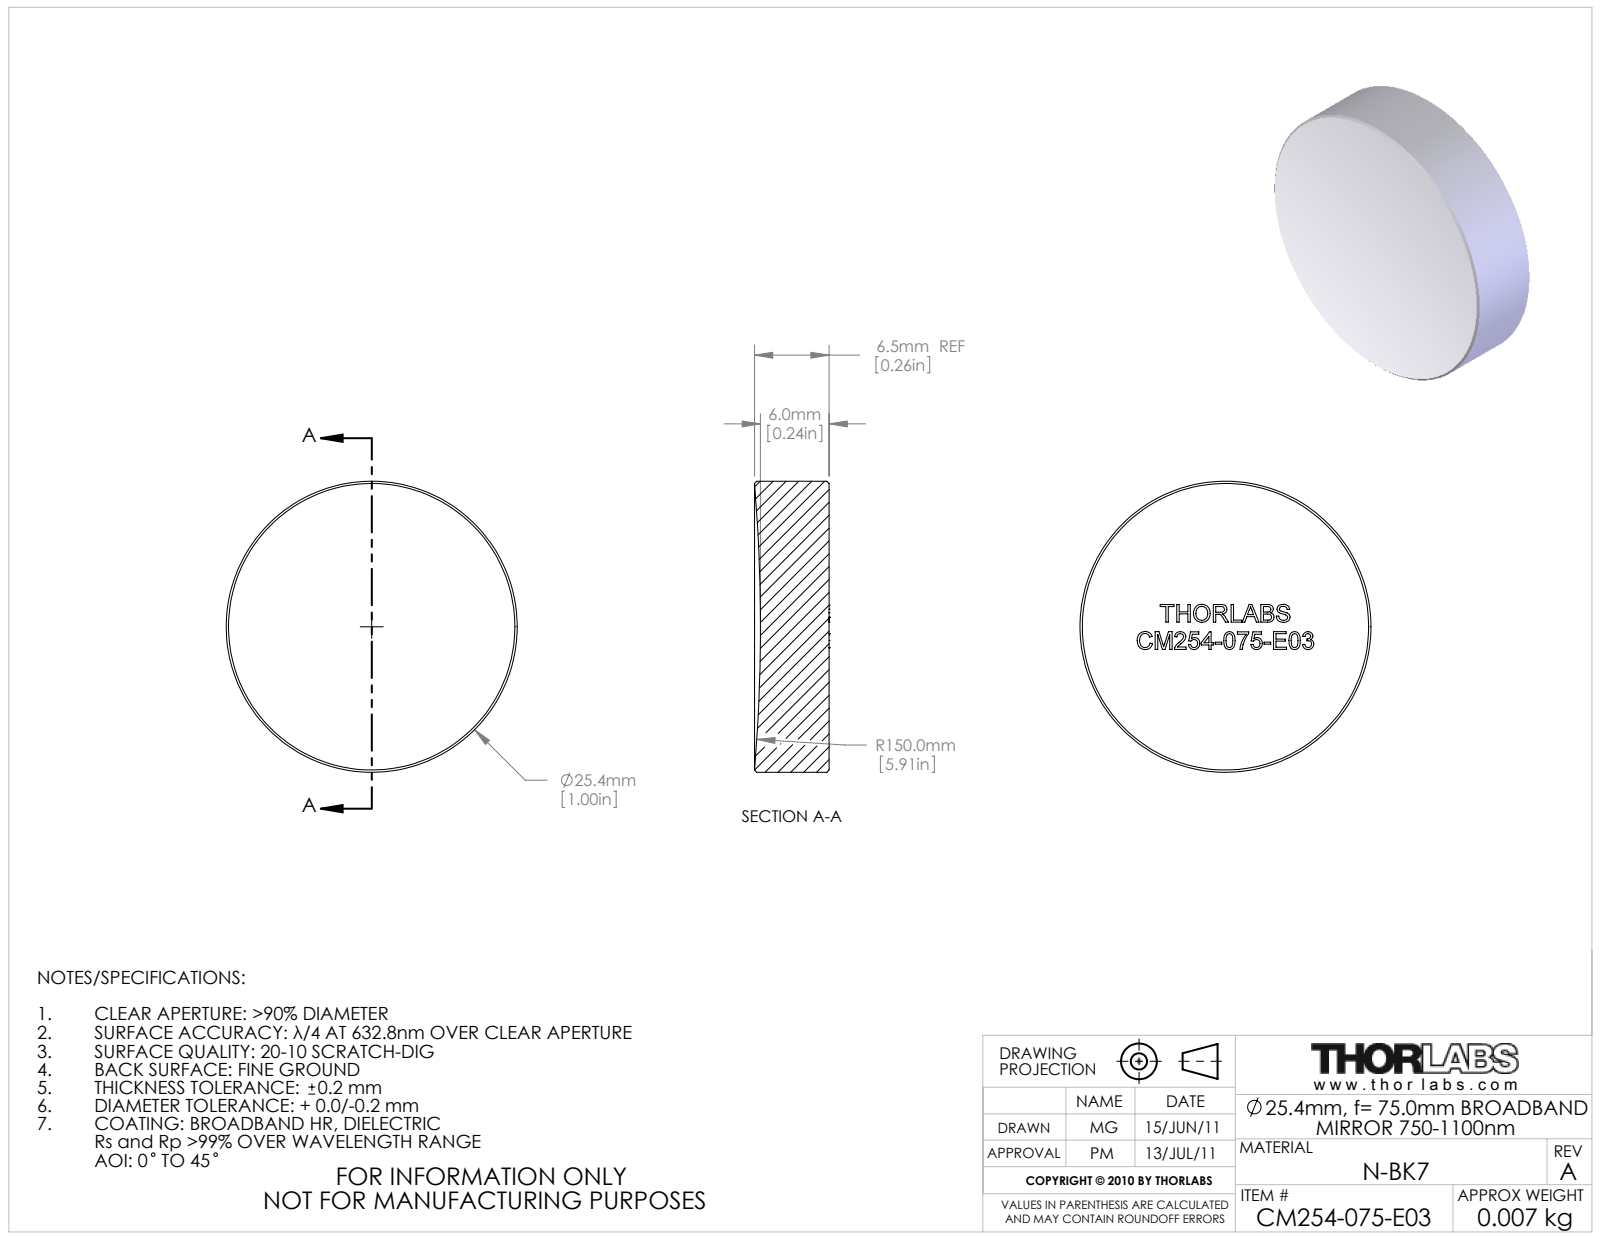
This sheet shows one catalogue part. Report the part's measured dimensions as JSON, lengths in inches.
{"part_name": "22643-E0W", "step_written_by": "SolidWorks 2011 (AUTOMOTIVE_DESIGN)", "units": "inches", "bodies": {"solids": 0, "faces": 39, "planar": 30, "cylindrical": 2, "other": 7}, "overall_size": [1, 1, 0.257], "round_bosses_or_shafts": [[1, 1]]}
